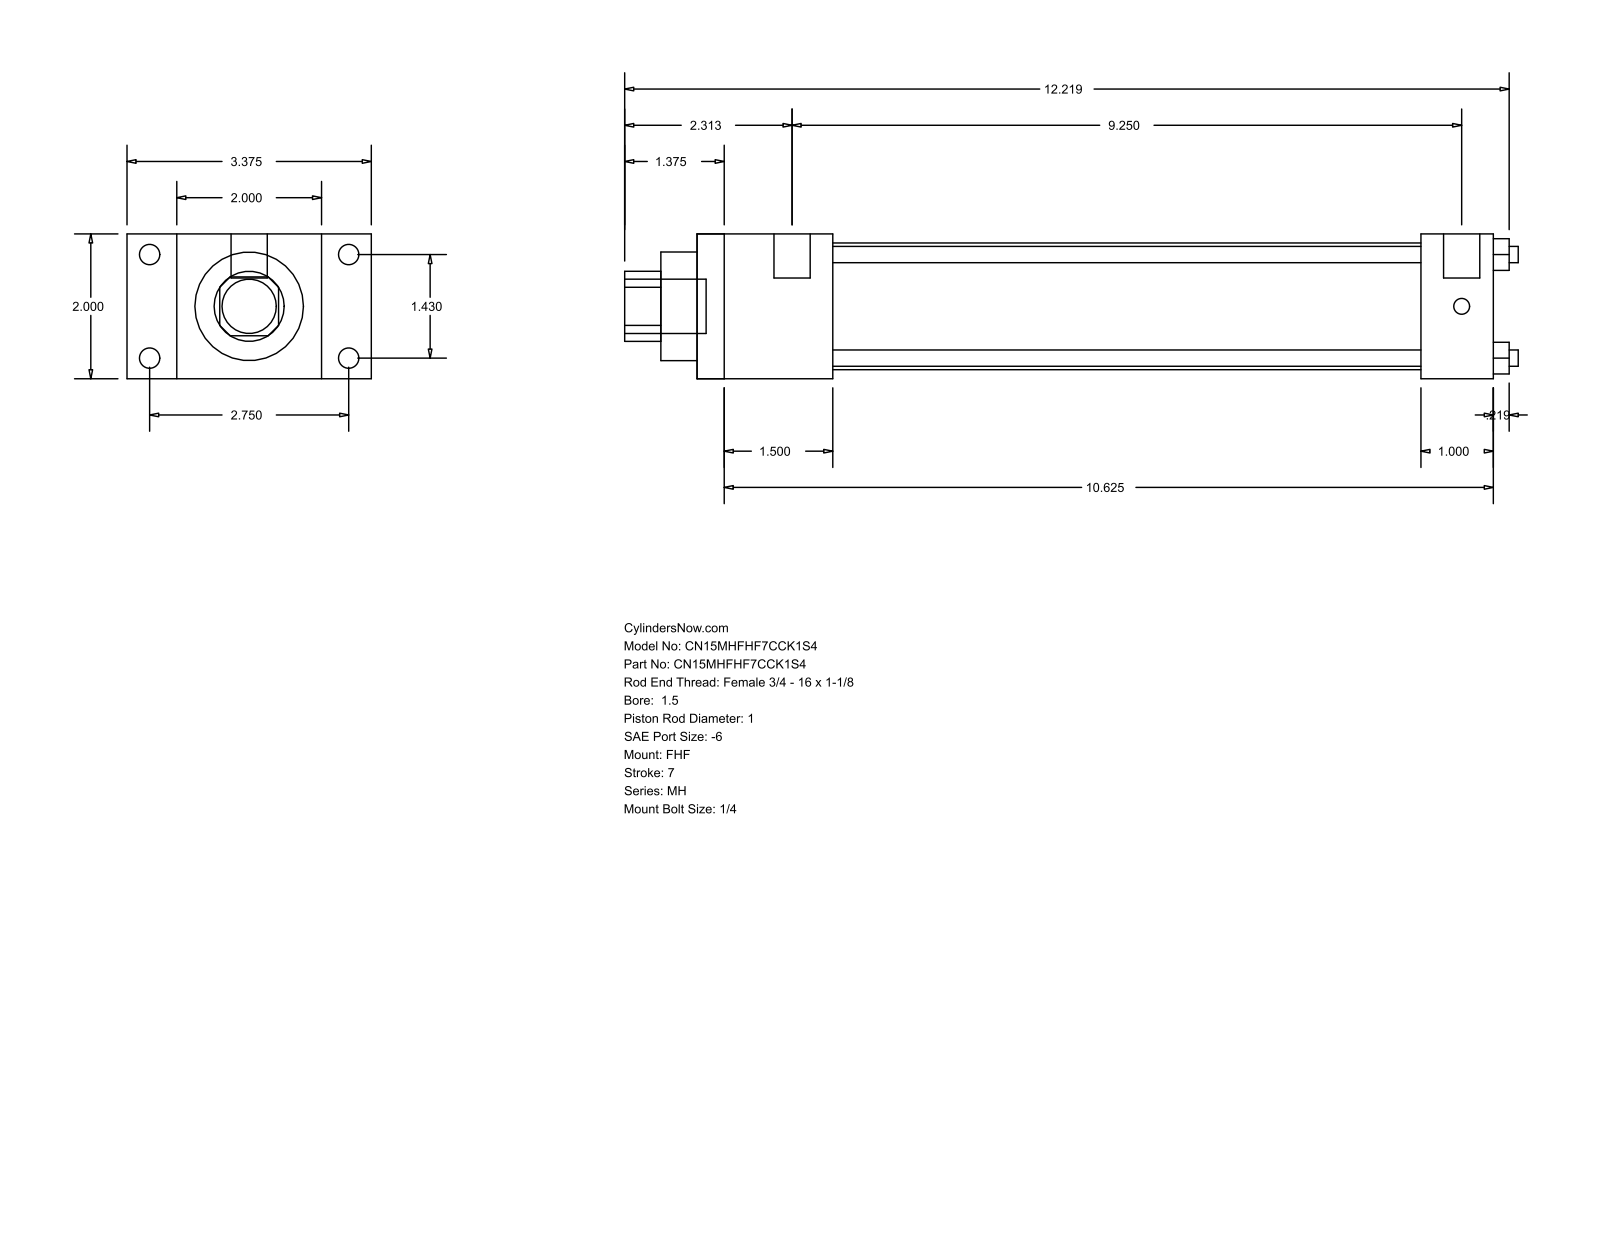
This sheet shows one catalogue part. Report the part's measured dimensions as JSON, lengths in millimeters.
{"part_name": "MH_FHF__0150_1", "step_written_by": "GSSL Pune (CONFIG_CONTROL_DESIGN)", "units": "millimeters", "bodies": {"solids": 0, "faces": 88, "planar": 60, "cylindrical": 28, "other": 0}, "overall_size": [313.53, 85.72, 50.8], "round_holes": [[5.71, 4], [25.4, 1], [38.1, 1], [44.45, 1]], "round_bosses_or_shafts": [[7.14, 4], [5.56, 4], [12.7, 2], [19.05, 1]], "partial_cylinders_radius": [[12.29, 1]], "face_to_face_distances": [50.8, 17.46, 68.26, 47.63, 85.72, 279.4, 231.77, 25.4, 254, 206.37], "hole_center_spacings": [25.68, 36.32, 51.36]}
